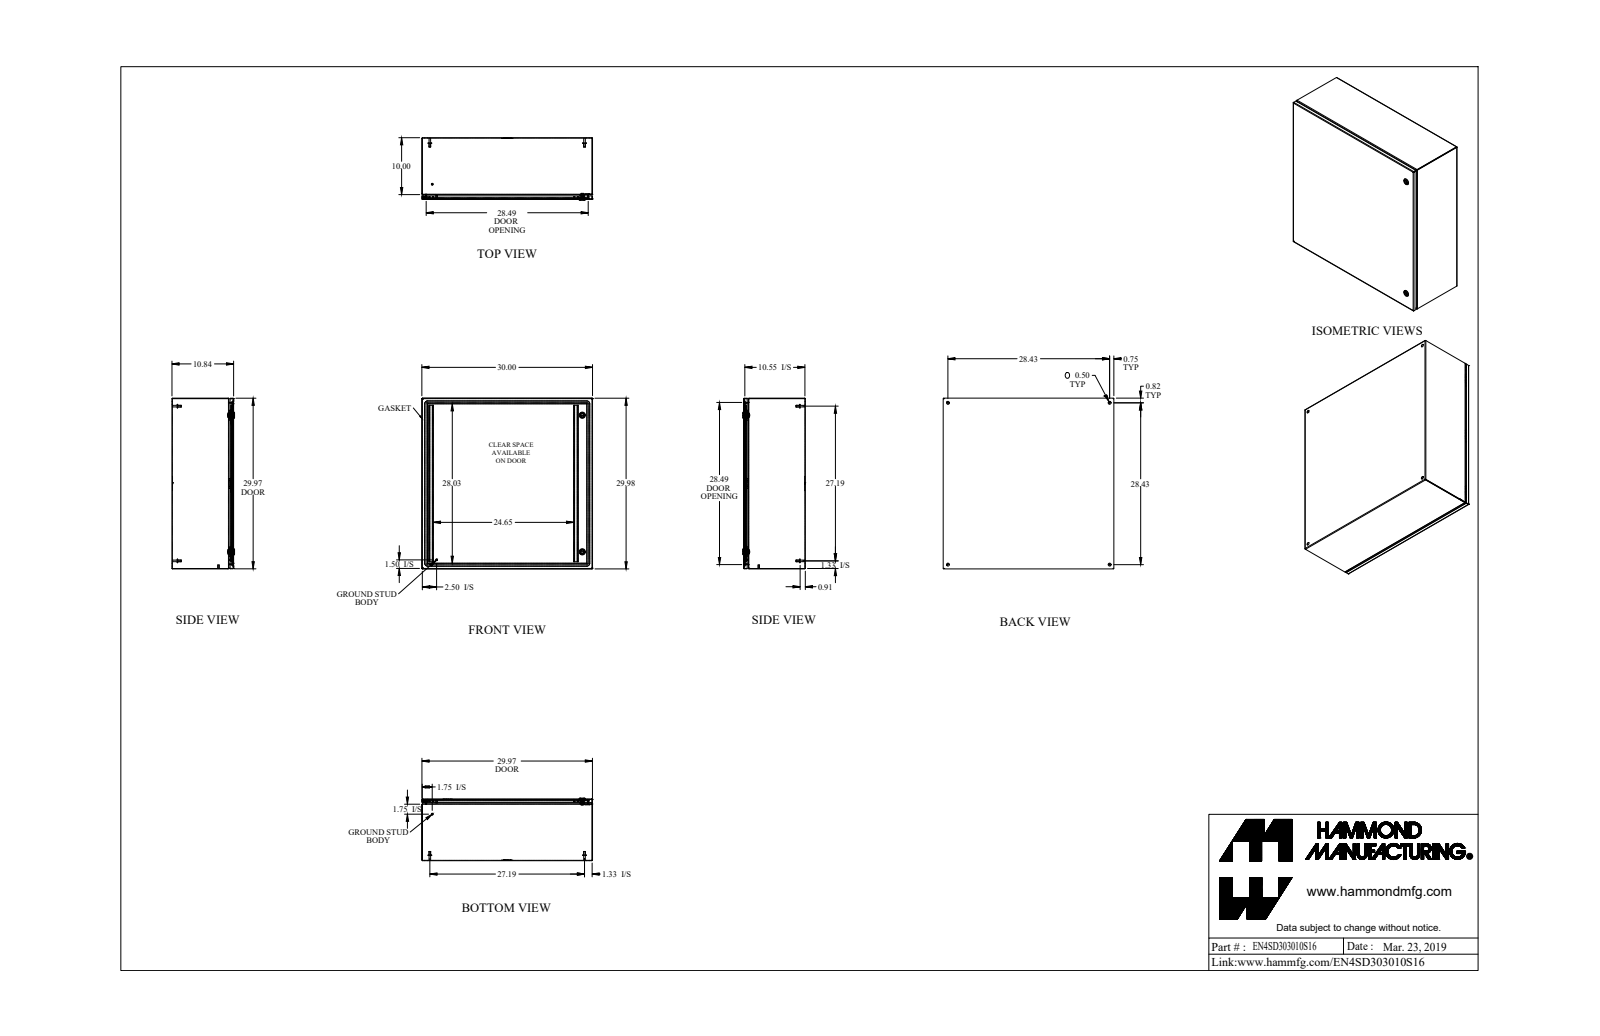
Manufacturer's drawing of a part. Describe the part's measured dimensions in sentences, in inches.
The part is named "EN4SD303010S16". Its 3-D file was written by "SolidWorks 2019 (AUTOMOTIVE_DESIGN)". It is 33 solids with 891 faces: 423 planar, 300 cylindrical and 168 other. Overall it measures 30 by 30 by 11.002 inches. Its volume is 248.2 cubic inches and its surface area 6 956 square inches. Round holes: 6 of diameter 0.5, 2 of diameter 0.197, 2 of diameter 0.387, 2 of diameter 0.63, 2 of diameter 0.768, 1 of diameter 0.172, 1 of diameter 0.24, 1 of diameter 0.242. Round bosses or shafts: 6 of diameter 0.625, 6 of diameter 0.313, 4 of diameter 0.275, 2 of diameter 1.1, 2 of diameter 0.785, 2 of diameter 0.525, 2 of diameter 0.25, 2 of diameter 0.236. Partial cylindrical surfaces (rounded edges, fillets, slot ends): 16 of radius 0.036, 16 of radius 0.108, 16 of radius 0.25, 12 of radius 0.01, 12 of radius 0.048, 8 of radius 0.1, 6 of radius 0.006, 6 of radius 0.062. The main face-to-face distances are 0.072, 10.77, 29.928, 10.698, 10.842, 29.856, 30, 0.842, 9.928, 0.75. The hole center spacings are 28.428, 40.203, 2.392, 2.458, 24, 26.196, 26.269, 27.525.
